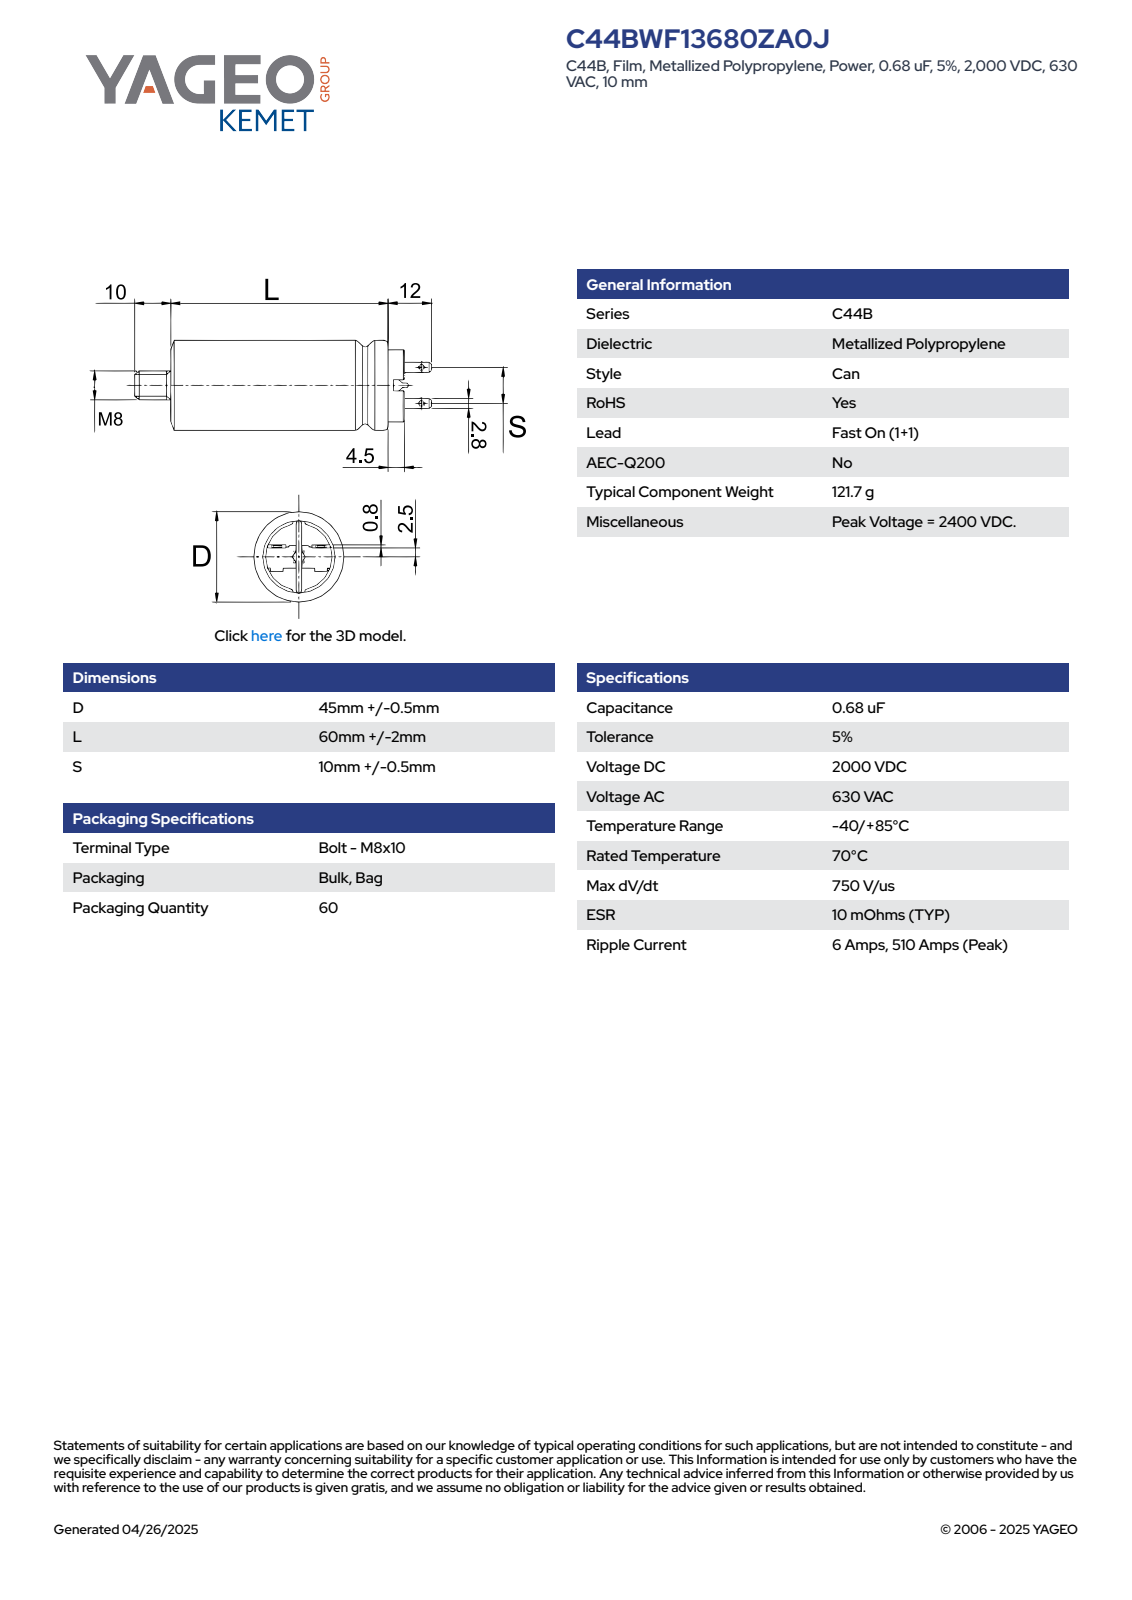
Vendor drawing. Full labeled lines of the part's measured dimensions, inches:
Part name (STEP PRODUCT): CFP_C44B_45X60_D45.5L62S10.5
STEP written by: SolidWorks 2014 (AUTOMOTIVE_DESIGN)
Units: inches
Bodies: 1 solid, 132 faces (49 planar, 40 cylindrical, 43 other)
Overall size (bounding box): 3.307 × 1.791 × 1.791
Volume: 6.166 in³ · Surface area: 21.5 in²
Round bosses / shafts (diameter × count): ⌀1.791 ×1, ⌀1.417 ×1, ⌀1.339 ×1, ⌀0.315 ×1
Partial cylindrical surfaces — rounded edges, fillets, slot ends (radius × count): R0.008 ×6, R0.027 ×1, R0.895 ×1
Main face-to-face distances: 2.441, 2.618, 0.177, 0.031, 0.394, 2.835, 3.012, 0.11, 0.413, 0.089
